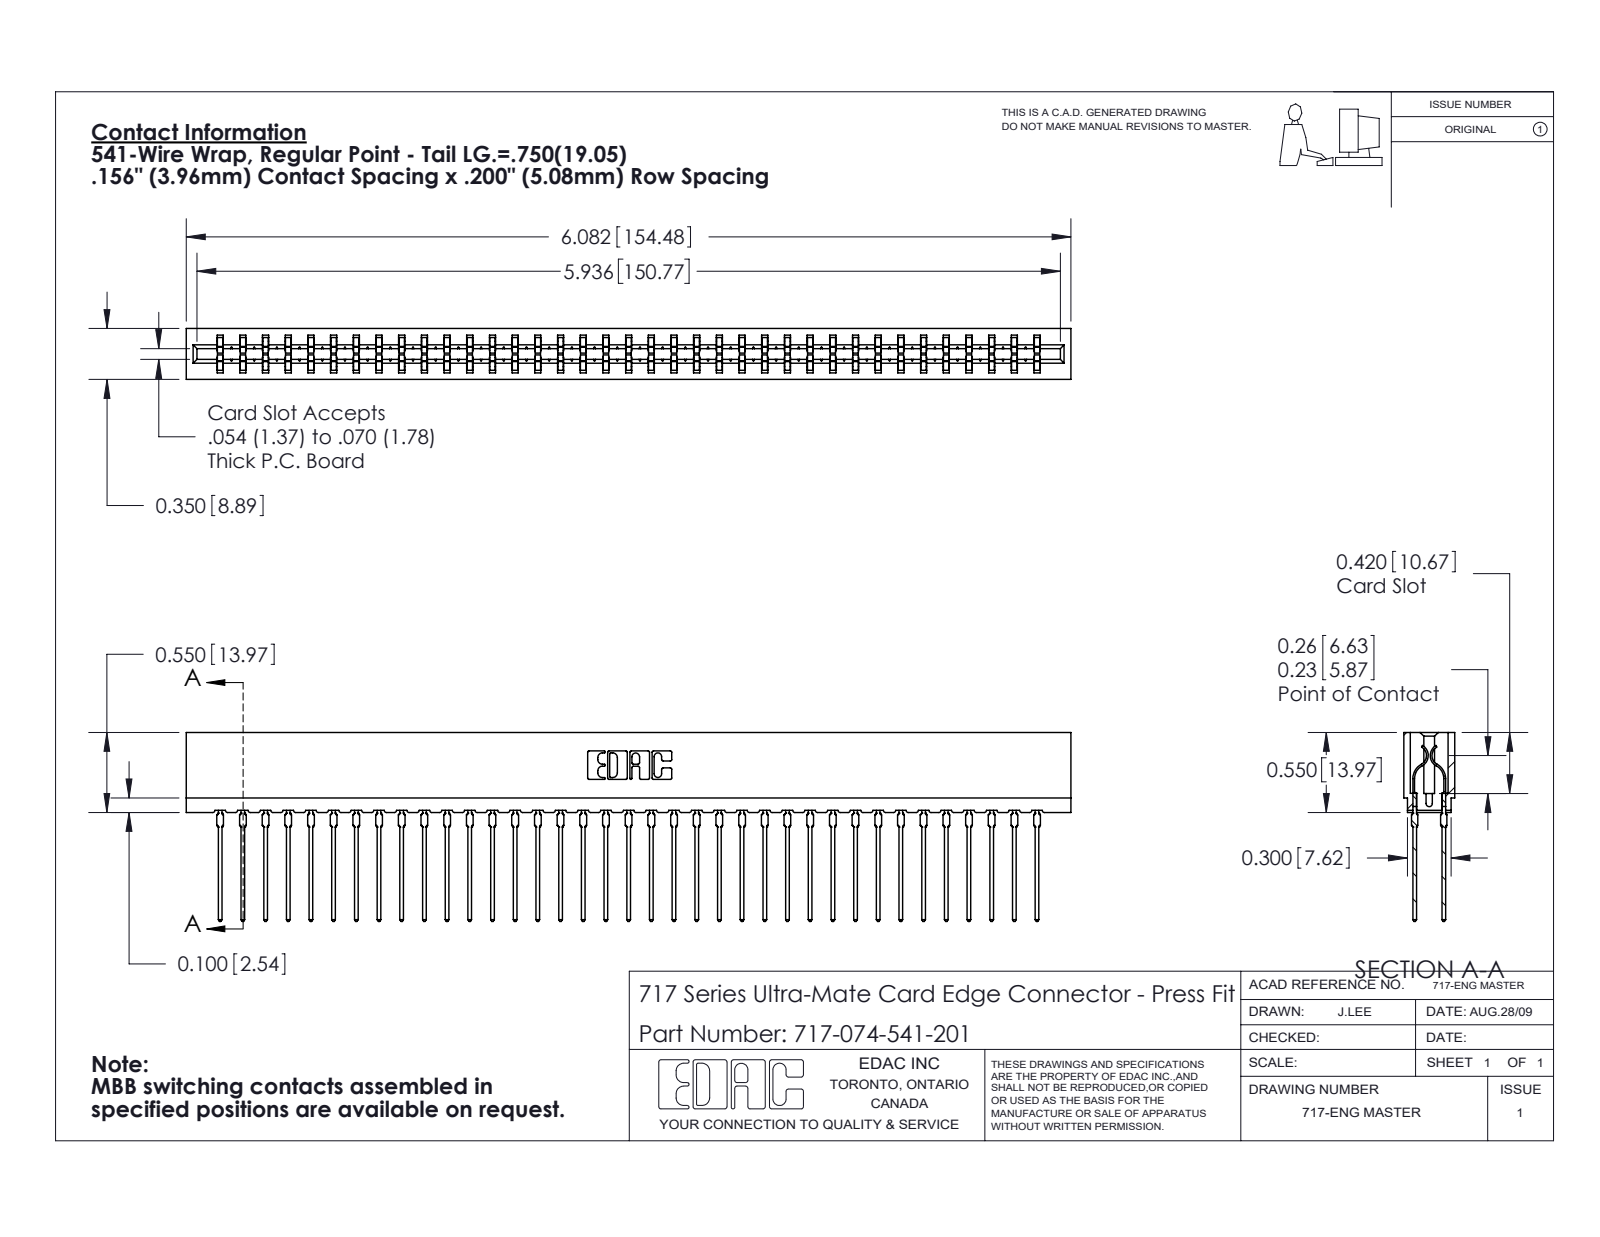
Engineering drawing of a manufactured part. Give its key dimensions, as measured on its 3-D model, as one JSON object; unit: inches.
{"part_name": "717-074-541-201; 717 Part_Insulator Option - 06; 745-292-001_541", "step_written_by": "SolidWorks 2020 (CONFIG_CONTROL_DESIGN)", "units": "inches", "bodies": {"solids": 75, "faces": 6754, "planar": 3495, "cylindrical": 1335, "other": 1924}, "overall_size": [6.082, 1.299, 0.35], "volume_in3": 0.84, "surface_area_in2": 35.1, "partial_cylinders_radius": [[0.021, 148], [0.015, 74], [0.01, 22], [0.005, 8], [0.011, 8], [0.007, 6], [0.031, 6], [0.026, 3]], "face_to_face_distances": [0.212, 0.138, 0.35, 0.063, 0.287, 0.076, 0.149, 0.087, 0.263, 0.025]}
